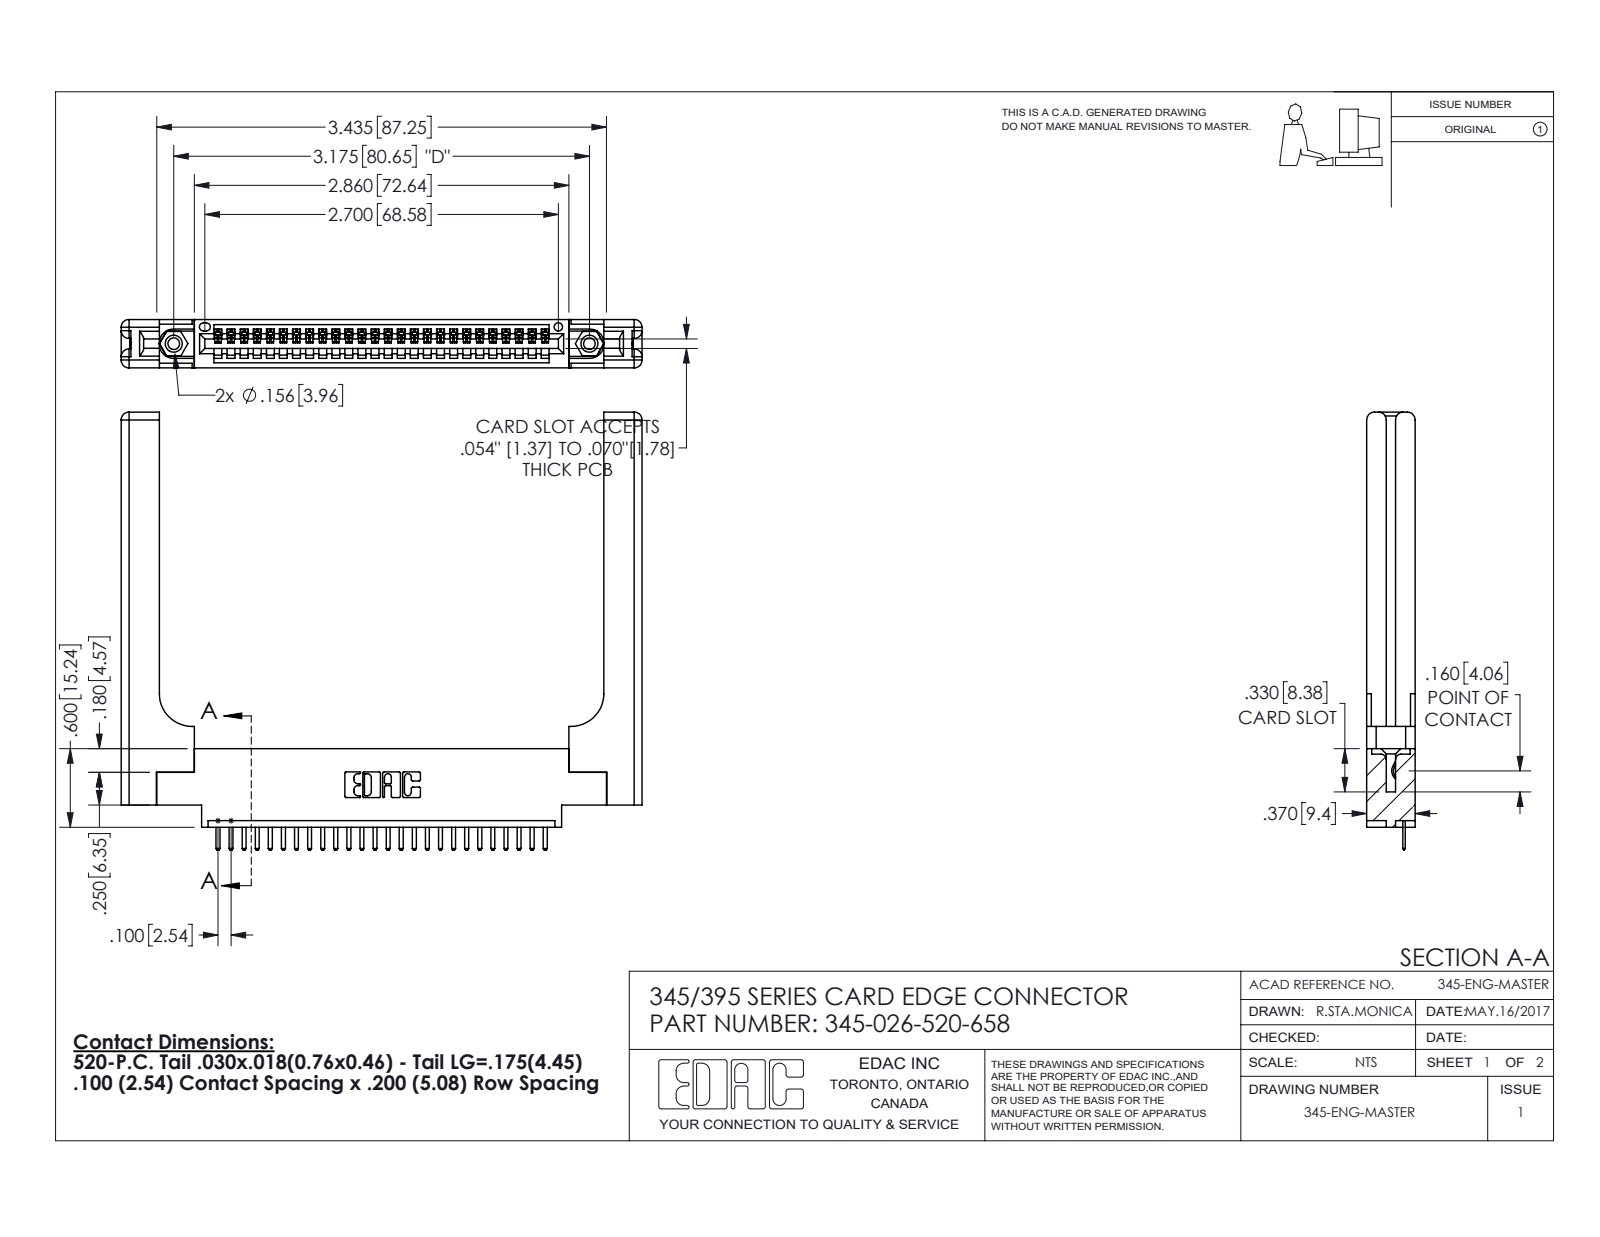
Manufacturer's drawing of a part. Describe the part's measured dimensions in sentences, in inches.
The part is named "345-250-001_345-250-001-102; 345-220-058_345-220-058; 345-026-520-658; 345 Part_0.170 Offset - 0.156 Dia-TH (+1 more)". Its 3-D file was written by "SolidWorks 2016 (CONFIG_CONTROL_DESIGN)". It is 31 solids with 1998 faces: 1324 planar, 614 cylindrical and 60 other. Overall it measures 3.979 by 3.345 by 0.37 inches. Its volume is 1.085 cubic inches and its surface area 26.82 square inches. Round holes: 2 of diameter 0.089, 2 of diameter 0.125, 2 of diameter 0.156, 1 of diameter 0.064. Round bosses or shafts: 2 of diameter 0.155. Partial cylindrical surfaces (rounded edges, fillets, slot ends): 54 of radius 0.01, 52 of radius 0.006, 22 of radius 0.01, 16 of radius 0.06, 6 of radius 0.007, 6 of radius 0.031, 3 of radius 0.026, 2 of radius 0.03. The main face-to-face distances are 0.37, 0.072, 0.298, 0.148, 0.15, 0.077, 0.22, 0.098, 0.272, 0.025. The hole center spacings are 0.27, 2.94, 3.175.
